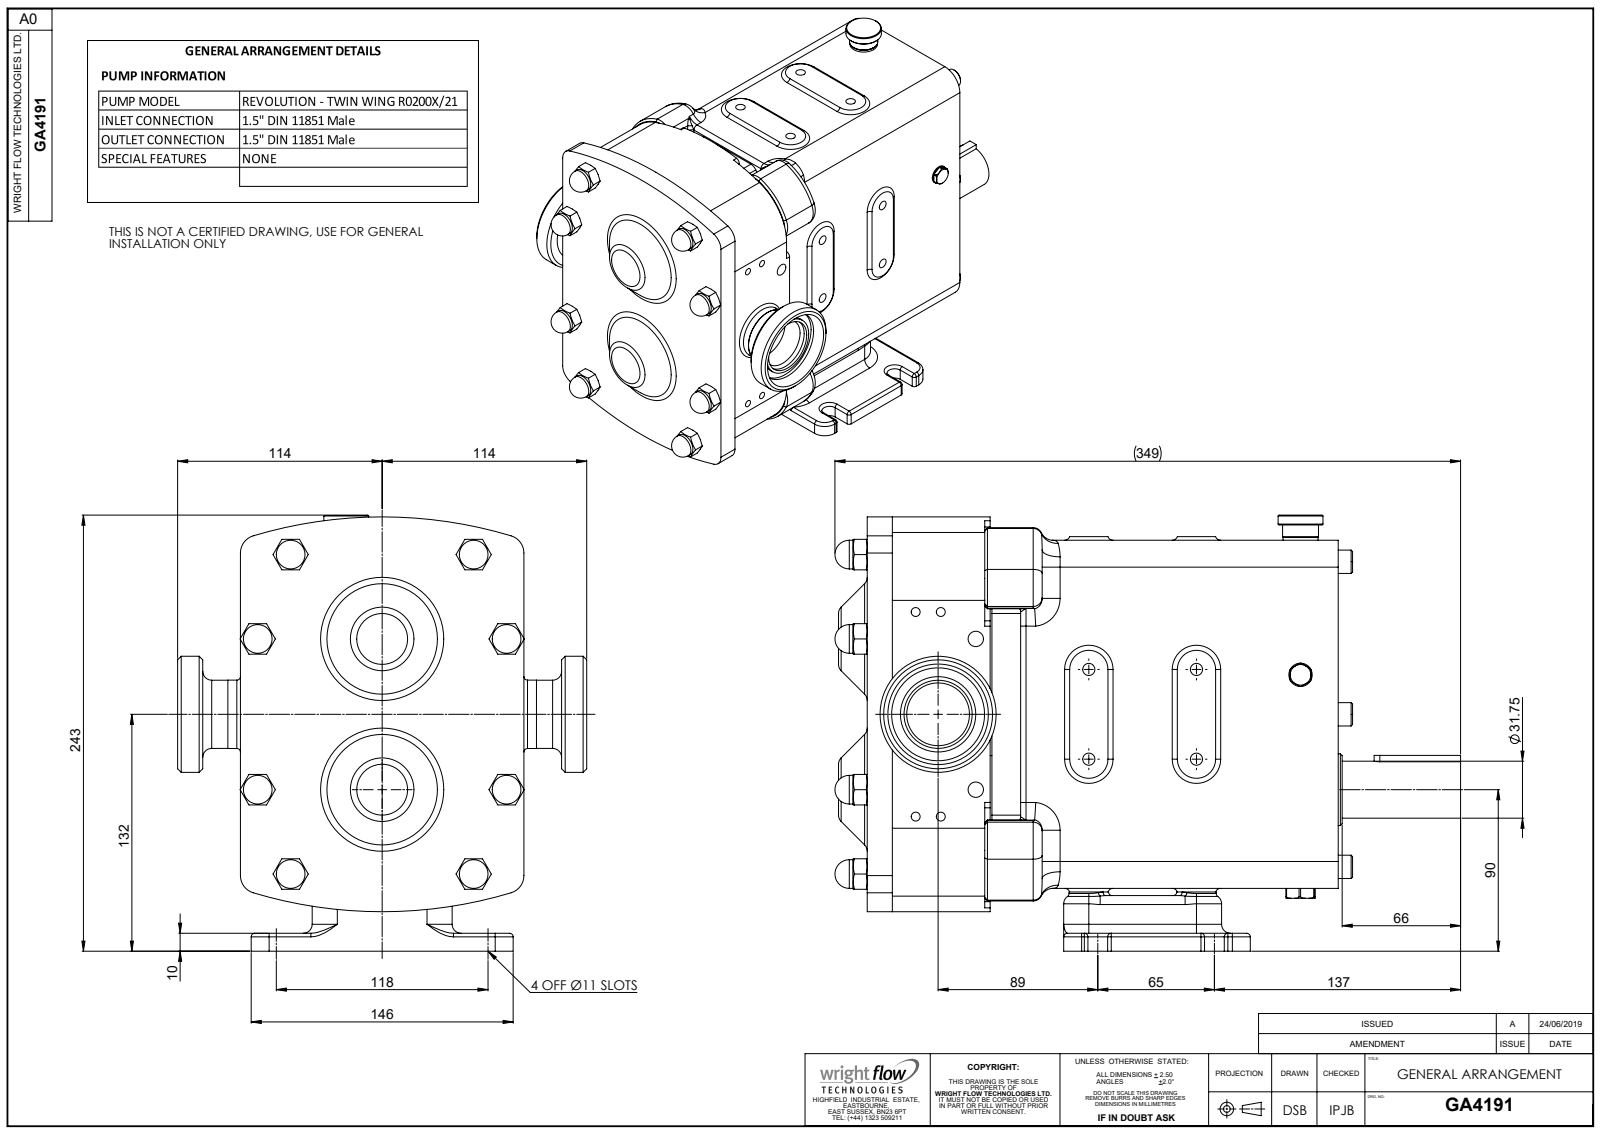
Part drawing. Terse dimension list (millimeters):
name: Copy of R0200 CPP H BSD^GA4191; GA4191; Copy of Z94-5031-22 - 1.5 INCH DIN11851^GA4191
written by: SolidWorks 2023 (AUTOMOTIVE_DESIGN)
unit: mm
bodies: 3 solids, 959 faces (299 planar, 308 cylindrical, 352 other)
size: 348.7 × 243 × 228
volume: 6 756 000 mm³; area: 369 482 mm²
holes: 8× ⌀6.8, 4× ⌀5, 2× ⌀8.6, 1× ⌀23, 1× ⌀35, 1× ⌀38, 1× ⌀51.8
bosses: 8× ⌀16, 7× ⌀13, 1× ⌀64.7, 1× ⌀42, 1× ⌀40, 1× ⌀38.1, 1× ⌀38, 1× ⌀31.75
rounds: 30× R10, 28× R3, 24× R2, 19× R5, 8× R5.9, 8× R15, 4× R5.5, 4× R8
face distances: 194, 68.5, 24, 110, 262.5, 193, 1, 69.5, 134, 22
hole spacings: 50, 60, 78.1, 14, 24.6, 36.7, 46.96, 57.02
